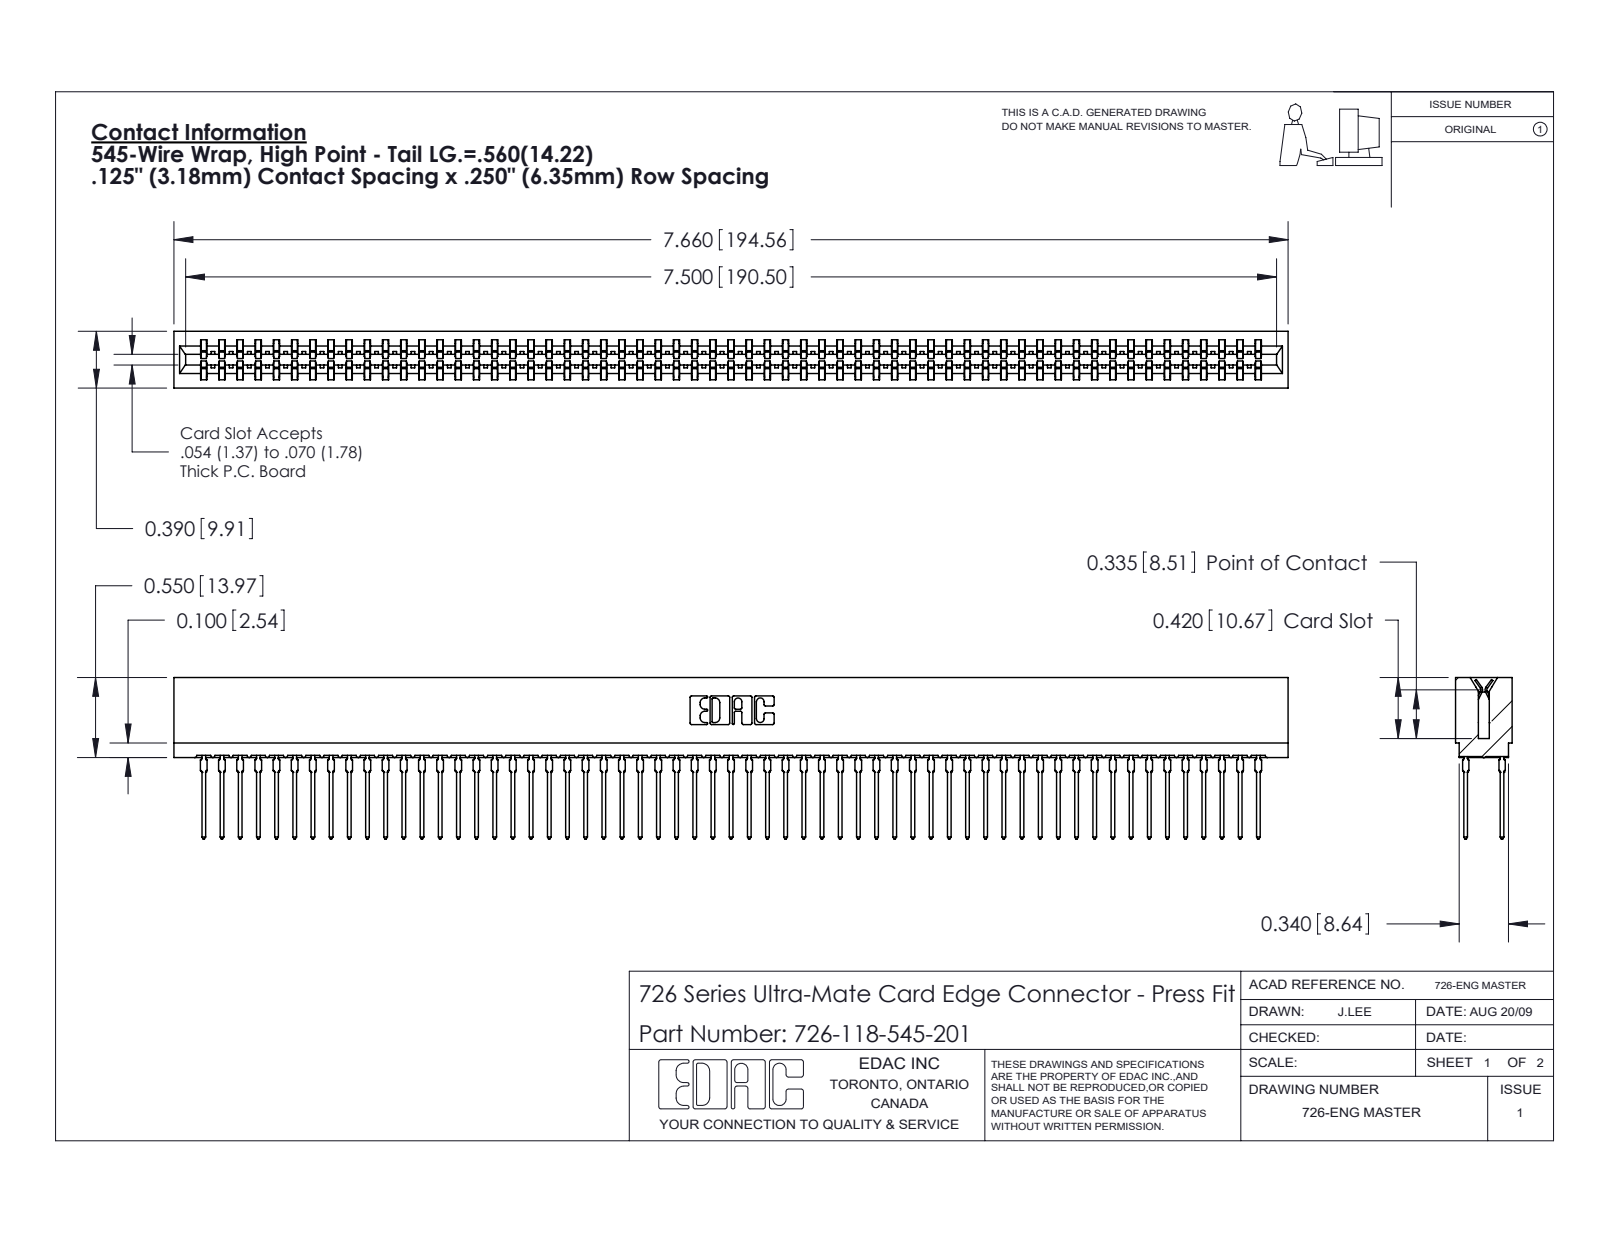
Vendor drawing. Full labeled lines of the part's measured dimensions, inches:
Part name (STEP PRODUCT): 746-292-001_545; 726-118-545-201; 726 Part_.515 Slot Depth - 01
STEP written by: SolidWorks 2020 (CONFIG_CONTROL_DESIGN)
Units: inches
Bodies: 119 solids, 10658 faces (5483 planar, 2107 cylindrical, 3068 other)
Overall size (bounding box): 7.66 × 1.109 × 0.39
Volume: 1.112 in³ · Surface area: 50.45 in²
Partial cylindrical surfaces — rounded edges, fillets, slot ends (radius × count): R0.021 ×236, R0.015 ×60, R0.01 ×22, R0.005 ×8, R0.011 ×8, R0.007 ×6, R0.031 ×6, R0.026 ×3
Main face-to-face distances: 0.057, 0.333, 0.025, 0.307, 0.25, 0.39, 0.275, 0.083, 0.365, 0.032
